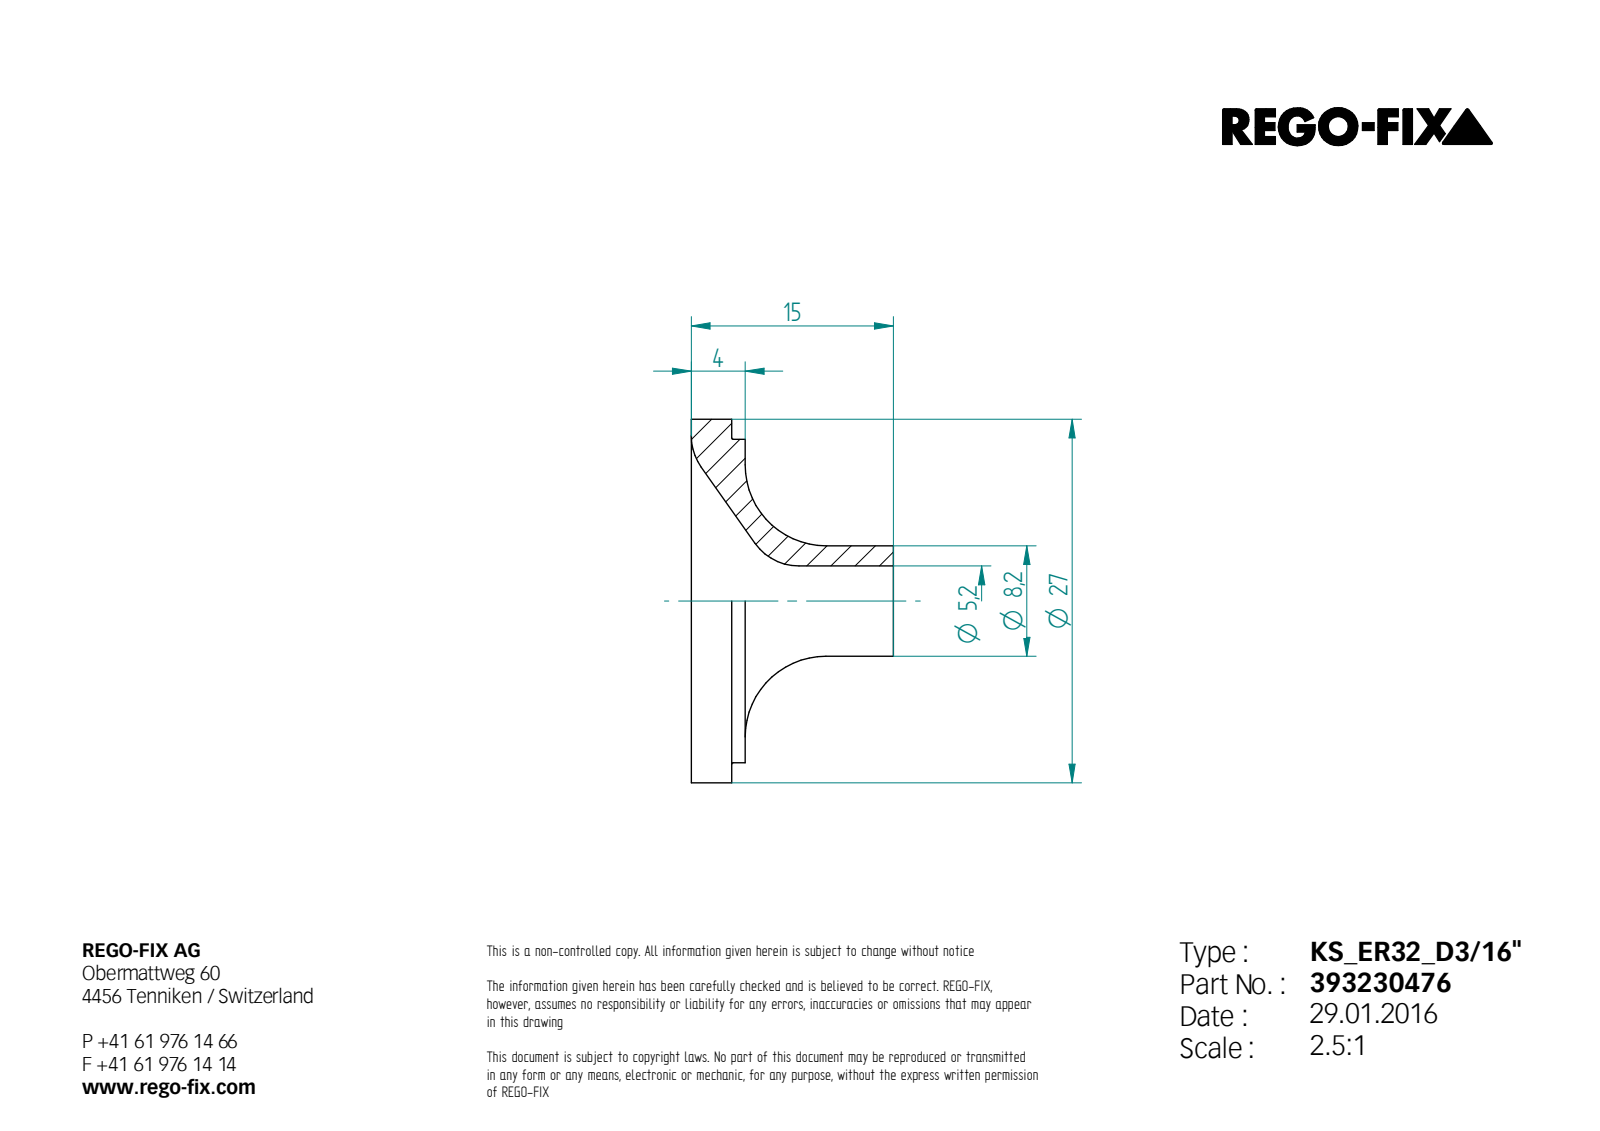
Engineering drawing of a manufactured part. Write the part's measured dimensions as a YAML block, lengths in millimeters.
step_written_by: "Unknown (AUTOMOTIVE_DESIGN)"
units: millimeters
bodies: {solids: 1, faces: 13, planar: 4, cylindrical: 4, other: 5}
overall_size: [27, 27, 15]
volume: 1832
surface_area: 1883
round_holes:
  - {diameter: 5.2, count: 1}
round_bosses_or_shafts:
  - {diameter: 27, count: 1}
  - {diameter: 24, count: 1}
  - {diameter: 8.2, count: 1}
face_to_face_distances: [1, 3, 4, 15, 12, 11]
